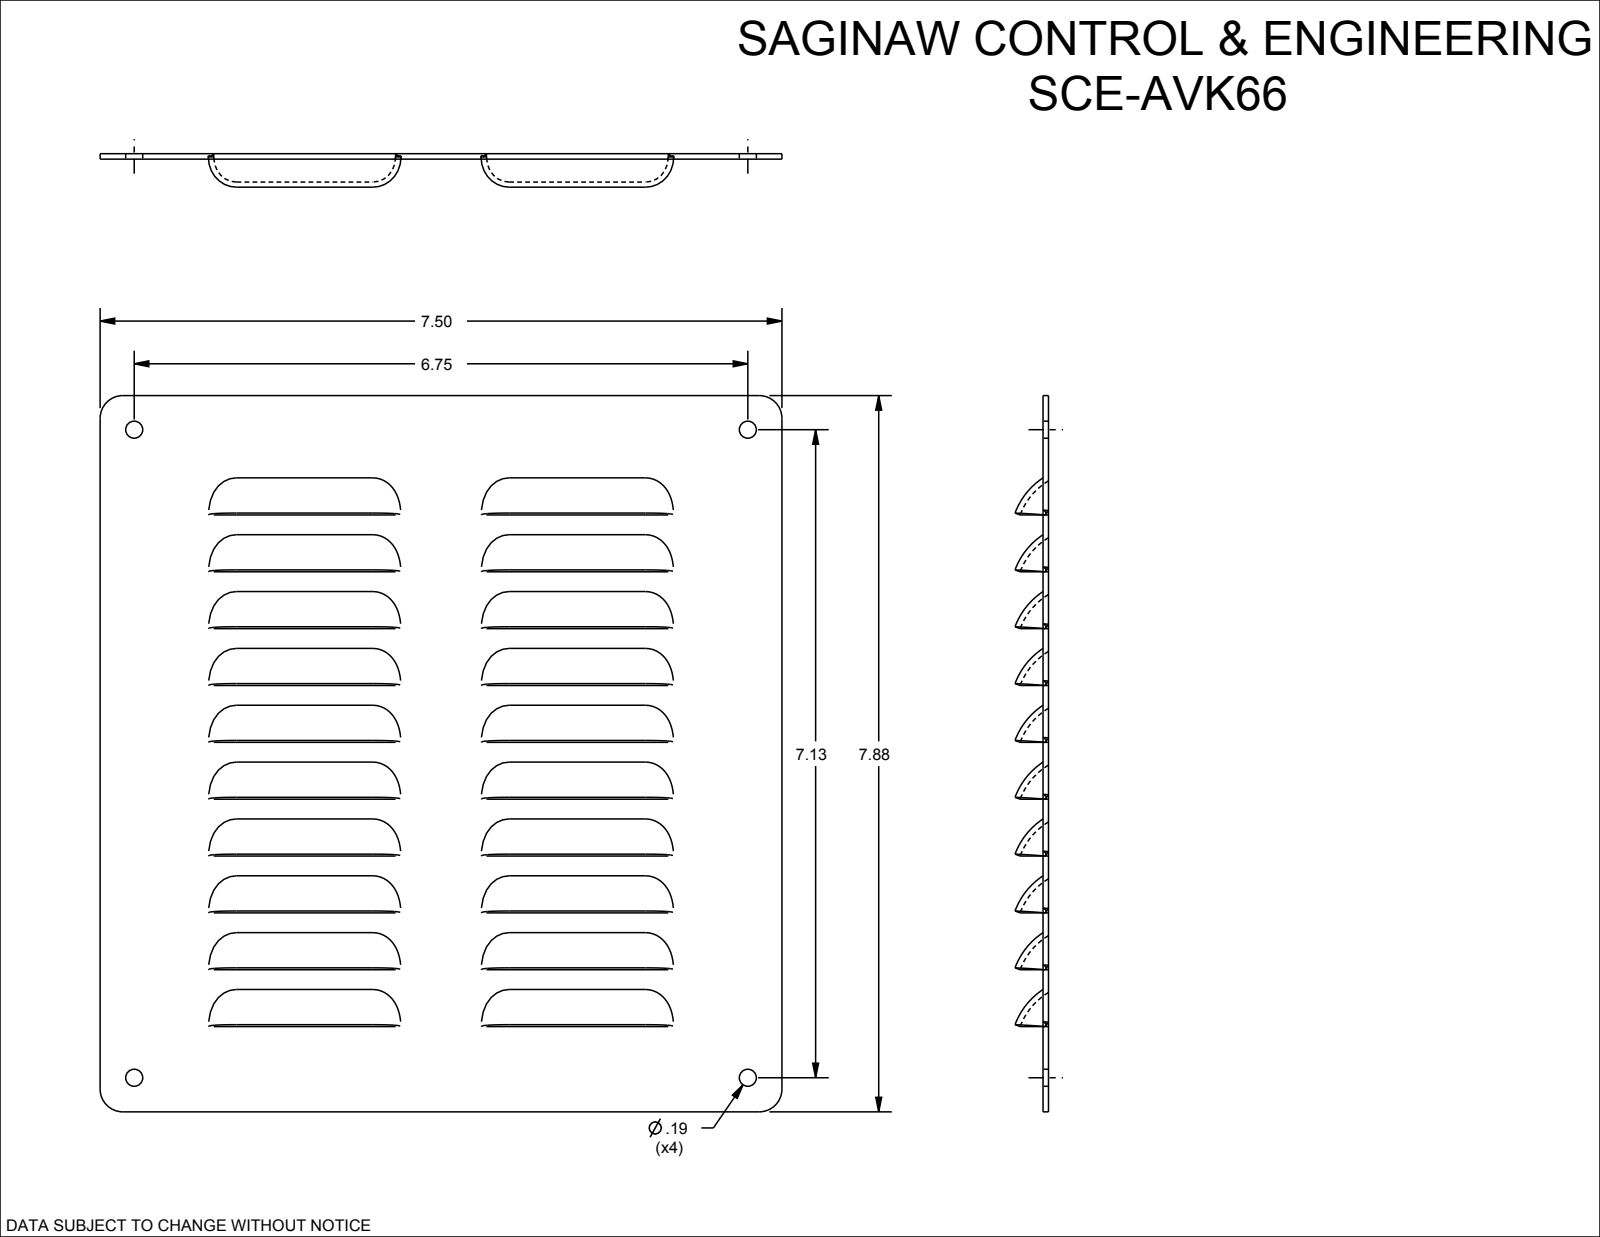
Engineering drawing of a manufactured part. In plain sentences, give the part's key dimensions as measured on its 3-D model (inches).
The part is named "SCE-AVK66". Its 3-D file was written by "SolidWorks 2021 (AUTOMOTIVE_DESIGN)". It is 1 solid with 318 faces: 66 planar, 92 cylindrical and 160 other. Overall it measures 7.875 by 7.5 by 0.467 inches. Its volume is 3.915 cubic inches and its surface area 137.1 square inches. Round holes: 4 of diameter 0.187. Partial cylindrical surfaces (rounded edges, fillets, slot ends): 10 of radius 0.74, 10 of radius 0.8, 4 of radius 0.25. The main face-to-face distances are 0.06, 1.25, 2.5, 3.75, 0.625, 0.625, 1.171, 0.29, 0.96, 1.875. The hole center spacings are 6.75, 7.125, 9.815.
